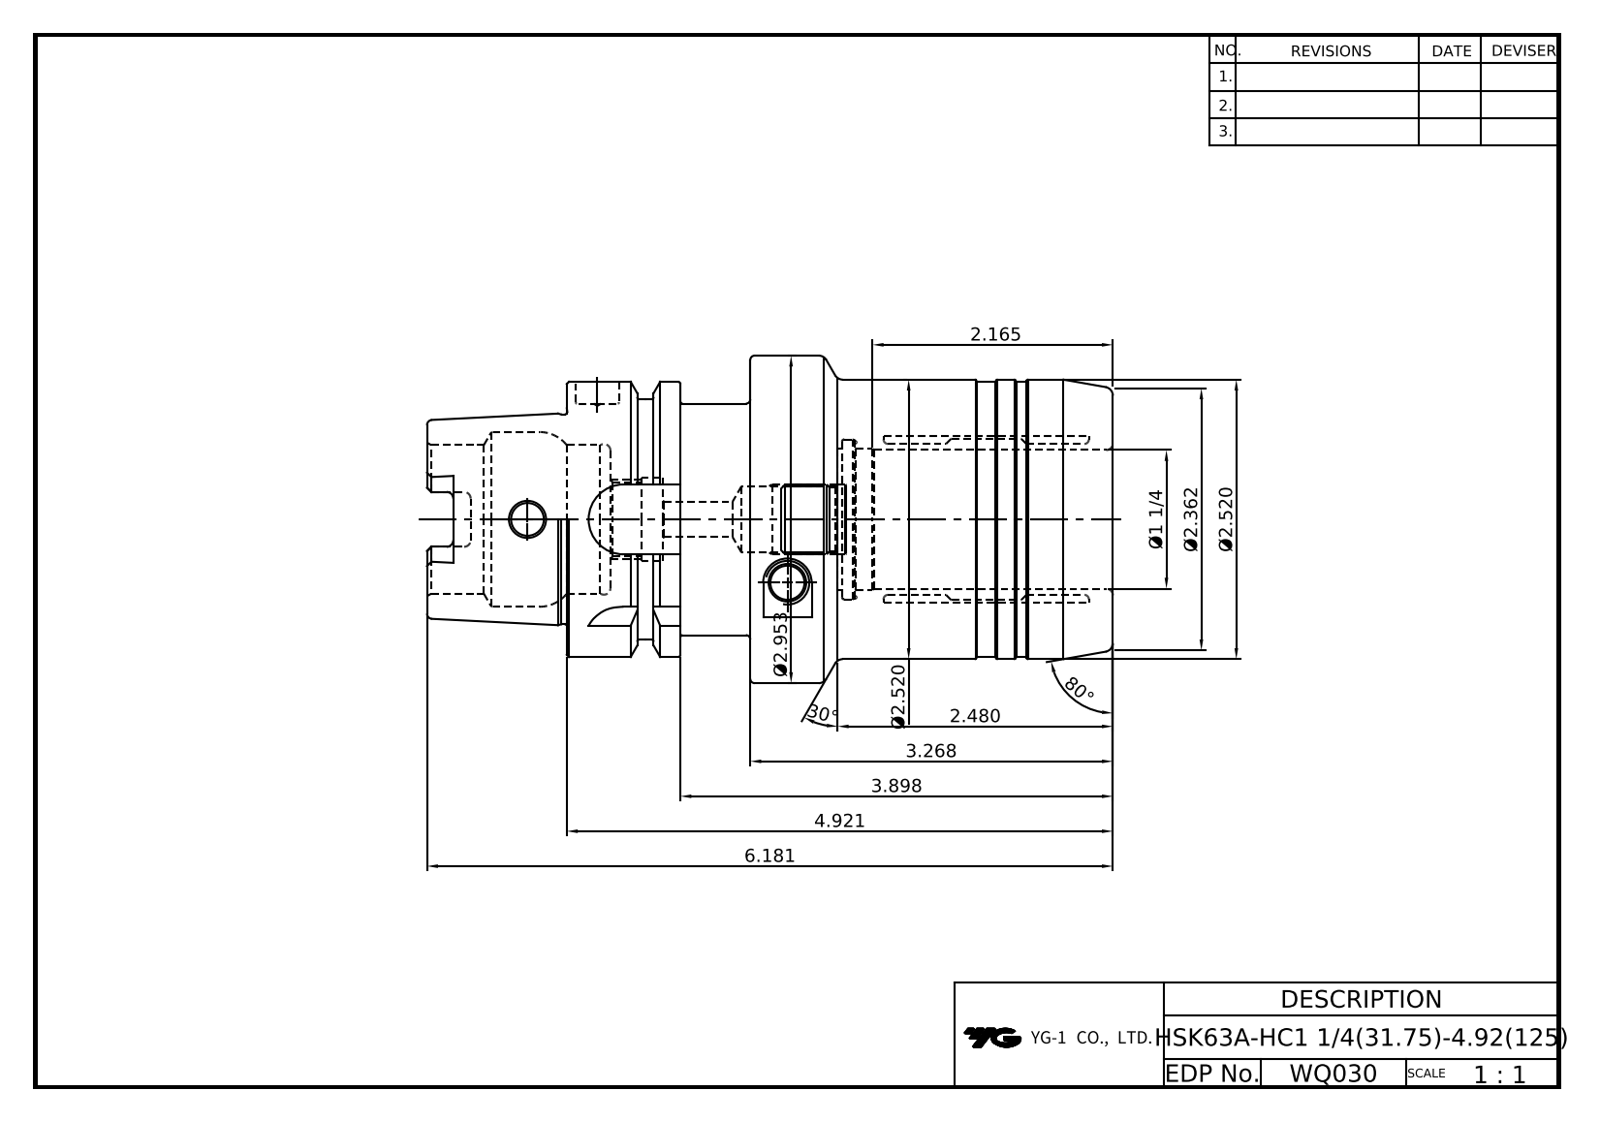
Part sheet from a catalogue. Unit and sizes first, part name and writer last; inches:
Units: inches
Overall size (bounding box): 6.181 × 2.952 × 2.952
Round holes (diameter × count): ⌀0.295 ×1, ⌀0.315 ×1, ⌀0.394 ×1, ⌀0.598 ×1, ⌀0.669 ×1, ⌀0.709 ×1, ⌀0.748 ×1, ⌀1.25 ×1, ⌀1.27 ×1, ⌀1.339 ×1, ⌀1.44 ×1, ⌀1.575 ×1
Round bosses / shafts (diameter × count): ⌀2.952 ×1, ⌀2.52 ×1, ⌀2.48 ×1, ⌀2.48 ×1, ⌀2.165 ×1, ⌀2.086 ×1, ⌀1.891 ×1
Partial cylindrical surfaces — rounded edges, fillets, slot ends (radius × count): R0.059 ×6, R0.113 ×4, R0.315 ×4
Main face-to-face distances: 3.267, 1.654, 0.63, 1.26, 4.921, 0.787, 1.024, 1.417, 2.047, 0.394
Volume: 21.18 in³ · Surface area: 83.98 in²
Bodies: 1 solid, 229 faces (60 planar, 67 cylindrical, 102 other)
Part name (STEP PRODUCT): WQ030-HSK63A-HC1_25-4_92
STEP written by: PRO/ENGINEER BY PARAMETRIC TECHNOLOGY CORPORATION, 2012130 (CONFIG_CONTROL_DESIGN)
